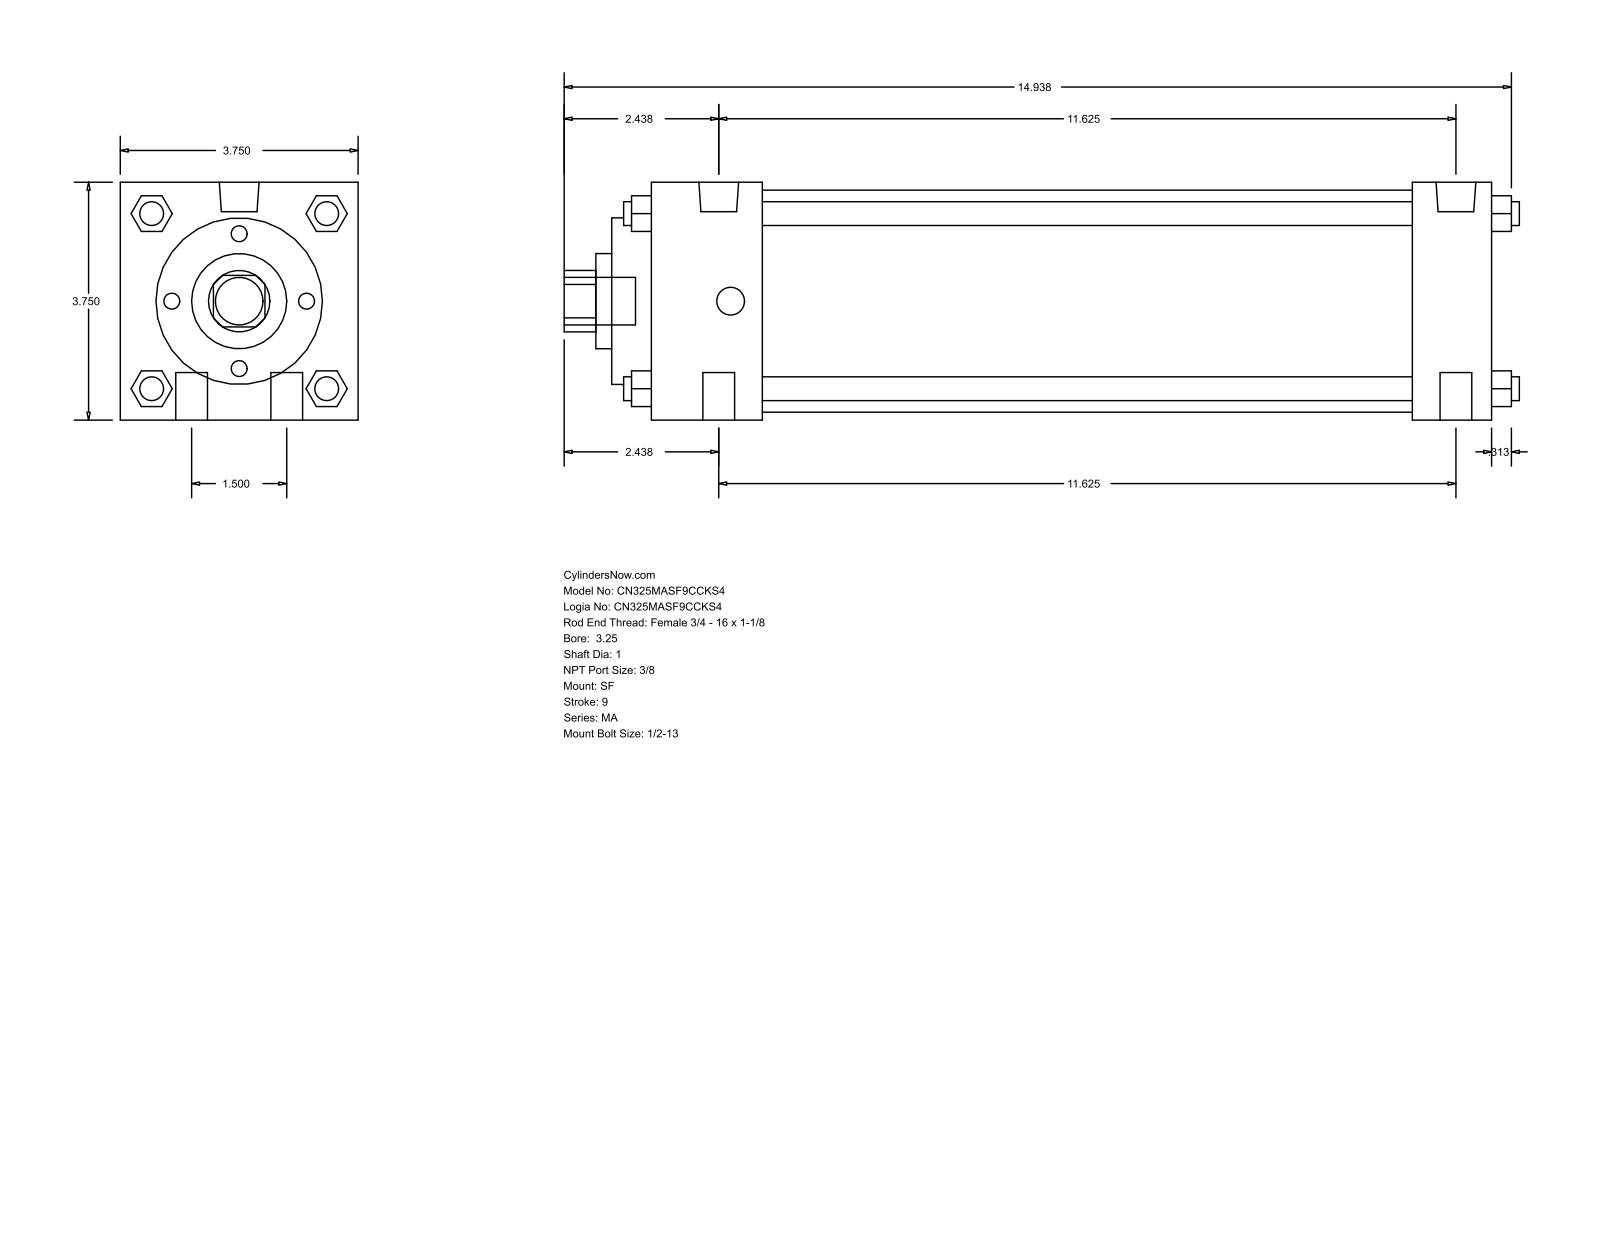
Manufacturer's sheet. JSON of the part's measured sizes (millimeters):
{"part_name": "MA_SF__0325_1", "step_written_by": "GSSL Pune (CONFIG_CONTROL_DESIGN)", "units": "millimeters", "bodies": {"solids": 0, "faces": 126, "planar": 95, "cylindrical": 31, "other": 0}, "overall_size": [382.59, 95.25, 95.25], "round_holes": [[25.4, 1], [38.1, 1], [66.67, 1], [88.9, 1]], "round_bosses_or_shafts": [[12.7, 4], [9.53, 4], [15.93, 2], [11.11, 2], [19.05, 1]], "partial_cylinders_radius": [[12.29, 1]], "face_to_face_distances": [95.24, 336.56, 15.87, 304.81, 31.75, 44.46, 260.35, 292.1, 60.33, 320.68]}
